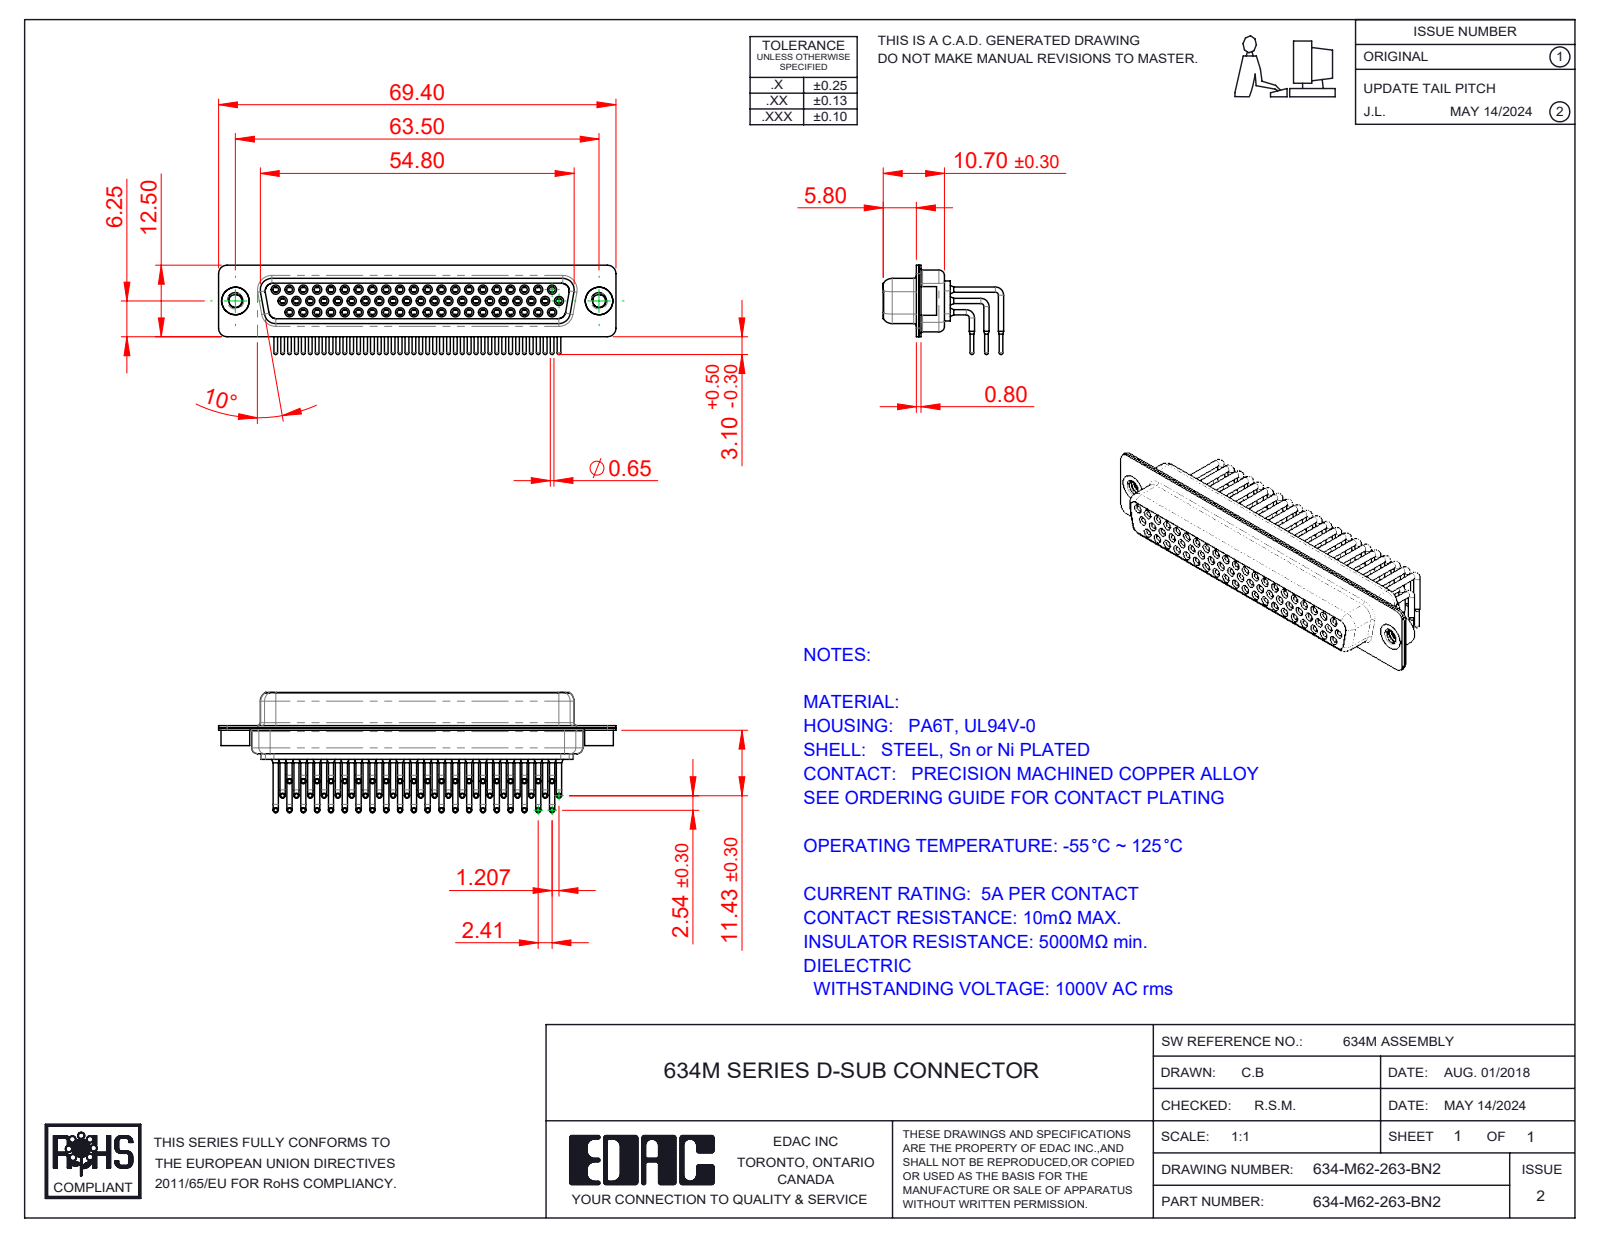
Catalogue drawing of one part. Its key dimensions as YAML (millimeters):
part_name: "634M 4-40 Threaded Rivet; 634M Contact Row 3; 634M Contact Row 2; 634-M62-263-BN2 (+4 more)"
step_written_by: "SolidWorks 2016 (CONFIG_CONTROL_DESIGN)"
units: millimeters
bodies: {solids: 67, faces: 3565, planar: 997, cylindrical: 1563, other: 1005}
overall_size: [69.4, 21.02, 15.6]
volume: 5405
surface_area: 17868
round_holes:
  - {diameter: 1, count: 62}
  - {diameter: 1.1, count: 62}
  - {diameter: 1.7, count: 62}
  - {diameter: 1.8, count: 62}
  - {diameter: 2, count: 62}
  - {diameter: 2.26, count: 2}
  - {diameter: 4, count: 2}
  - {diameter: 4.8, count: 2}
round_bosses_or_shafts:
  - {diameter: 0.9, count: 124}
  - {diameter: 1.6, count: 62}
  - {diameter: 1.5, count: 62}
  - {diameter: 0.65, count: 62}
  - {diameter: 2, count: 56}
  - {diameter: 5, count: 2}
  - {diameter: 4.9, count: 2}
partial_cylinders:
  - {radius: 1.5, count: 16}
  - {radius: 2, count: 12}
  - {radius: 1.35, count: 8}
  - {radius: 1.6, count: 8}
  - {radius: 0.25, count: 4}
  - {radius: 0.5, count: 4}
  - {radius: 0.6, count: 4}
  - {radius: 0.65, count: 4}
face_to_face_distances: [0.4, 1.45, 8.95, 1.9, 8.5, 2.3, 6.2, 0.45, 7.05, 0.85]
hole_center_spacings: [7.24, 2.32, 2.41, 9.65, 4.13, 4.83, 16.89, 14.48]
